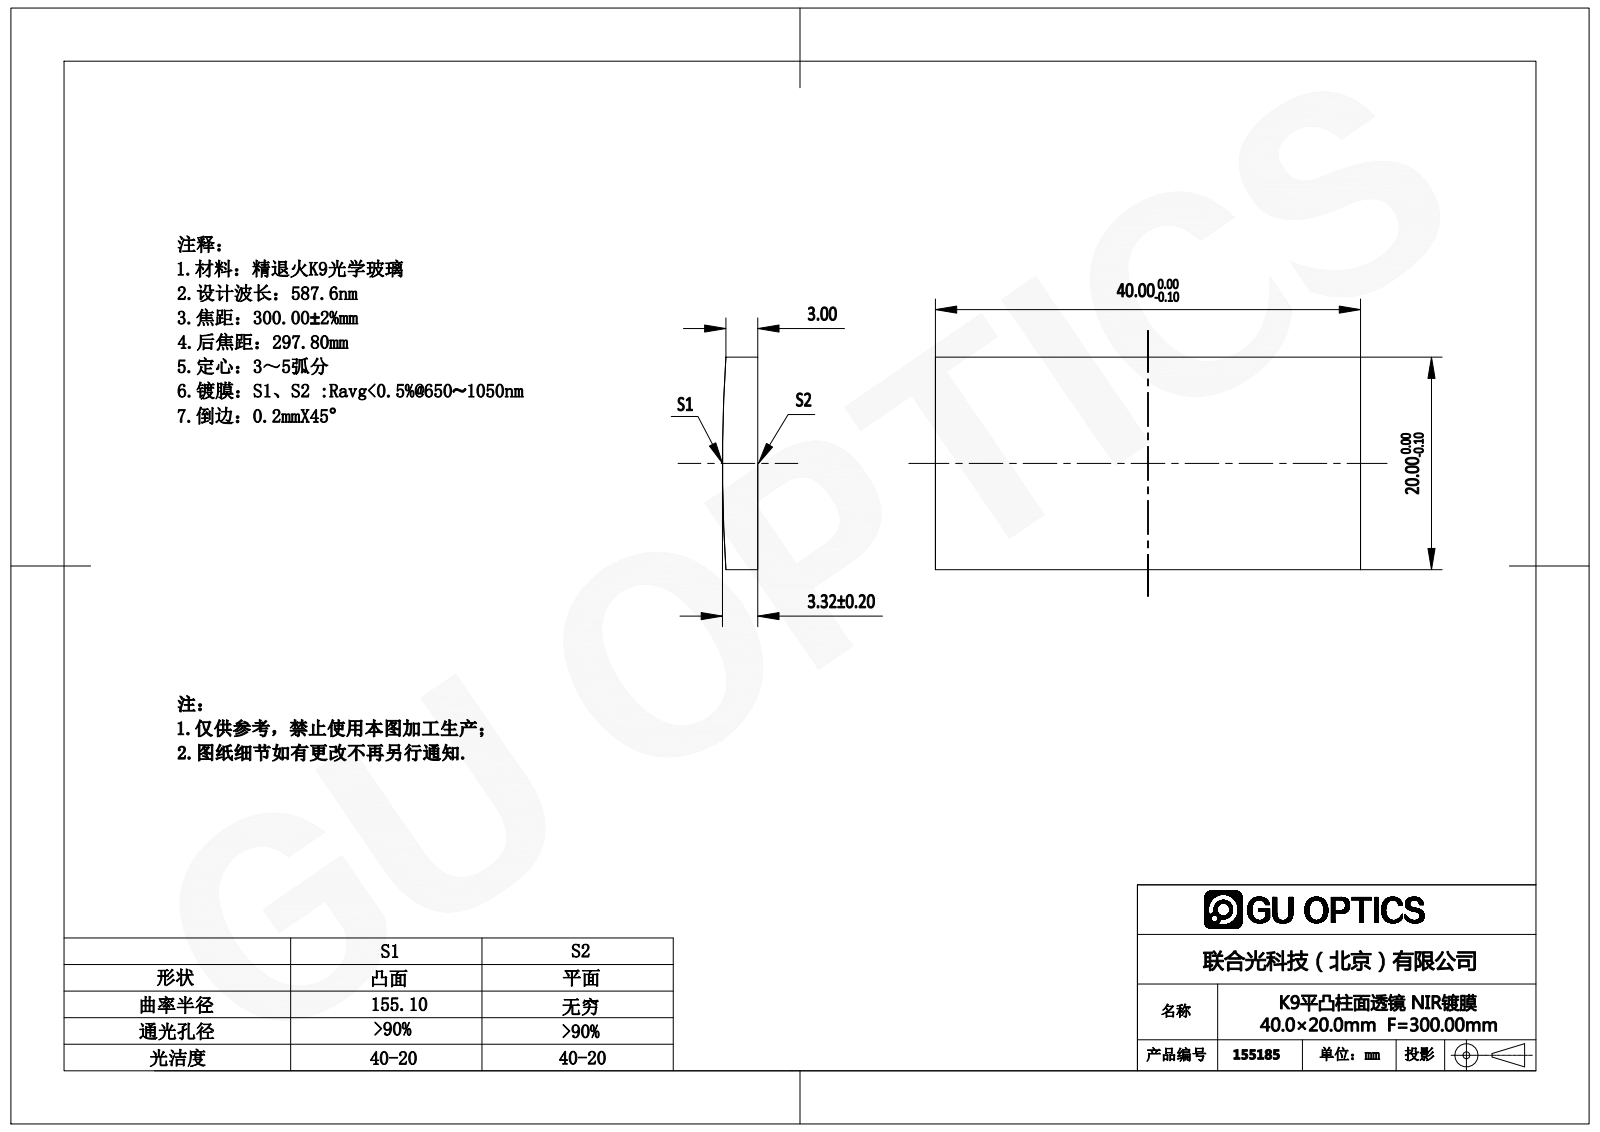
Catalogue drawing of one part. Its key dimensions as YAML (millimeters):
part_name: "155053"
step_written_by: "SolidWorks 2016 (AUTOMOTIVE_DESIGN)"
units: millimeters
bodies: {solids: 1, faces: 6, planar: 5, cylindrical: 1, other: 0}
overall_size: [40, 20, 3.32]
volume: 2570
surface_area: 1969
partial_cylinders:
  - {radius: 155.1, count: 1}
face_to_face_distances: [20, 40]
